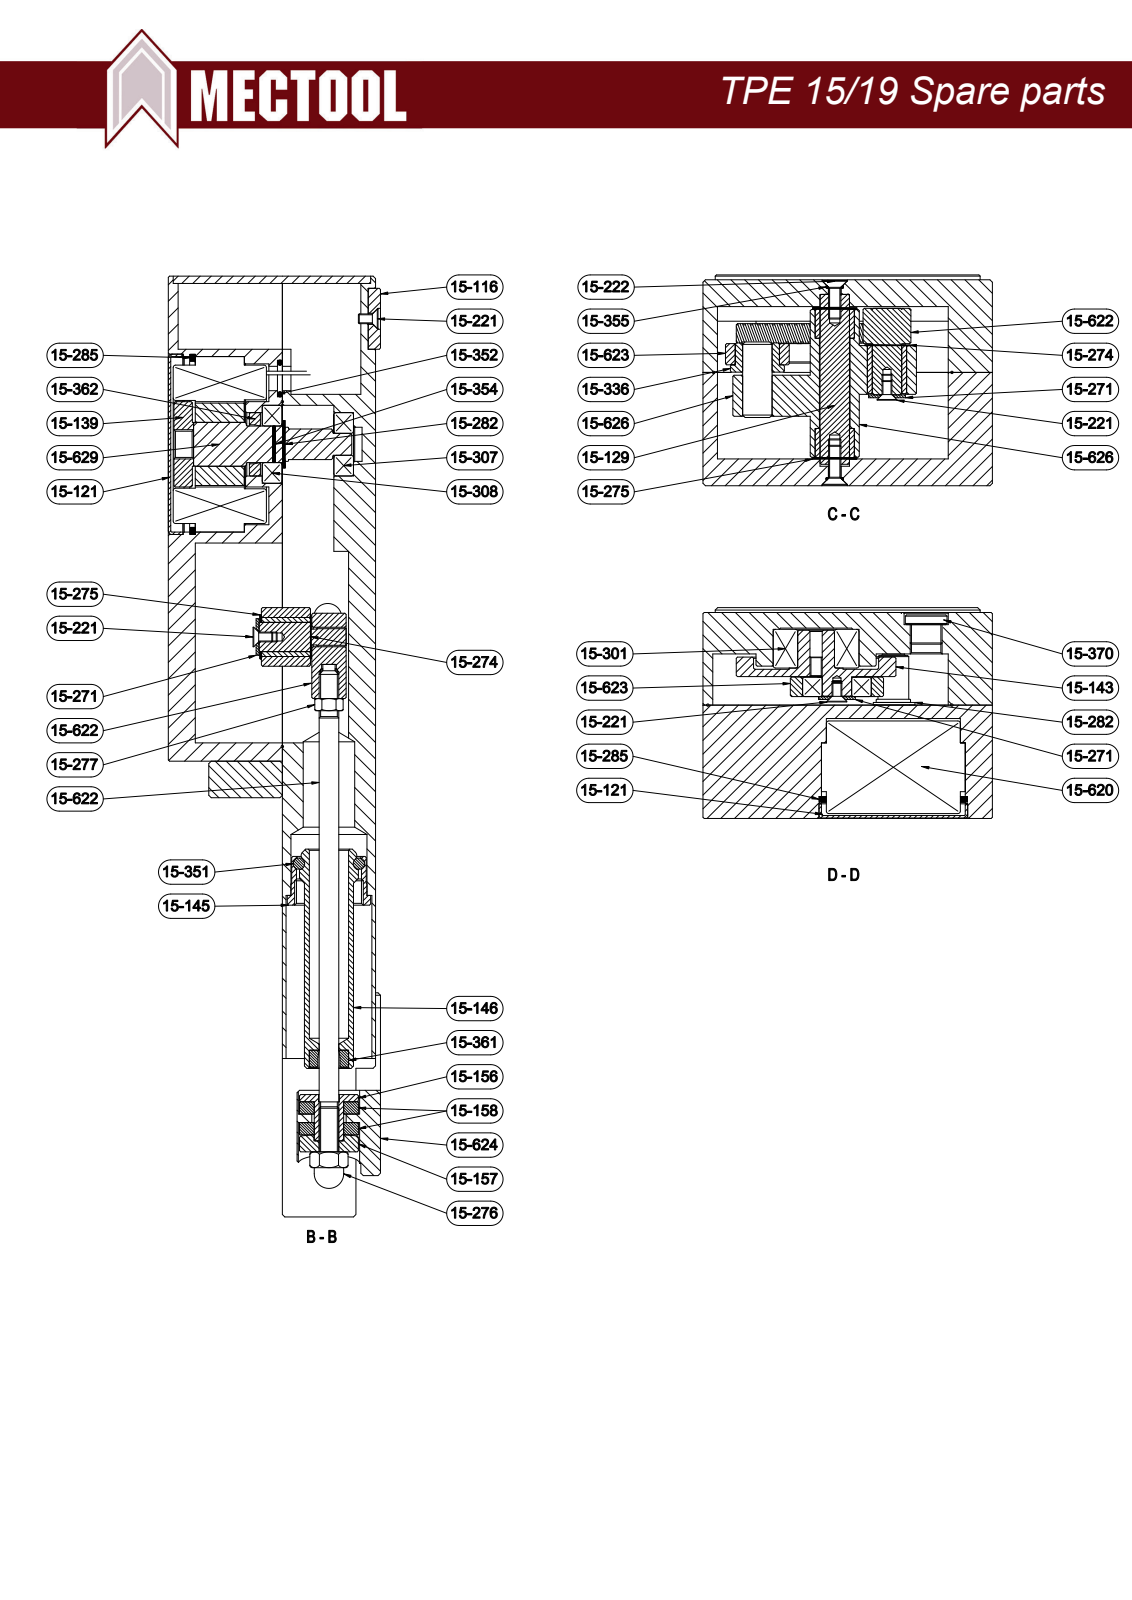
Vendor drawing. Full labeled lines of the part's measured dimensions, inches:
Part name (STEP PRODUCT): Nut : Dome - M8,0 x 162,052; Bolt : Hex - M4,0 x 12,0; Screw : Cheese - M6,0 x 10,0
STEP written by: Spatial InterOp 3D (automotive_design)
Units: inches
Bodies: 76 solids, 1832 faces (1675 planar, 128 cylindrical, 29 other)
Overall size (bounding box): 15.197 × 6.693 × 3.484
Volume: 162.7 in³ · Surface area: 545.2 in²
Round holes (diameter × count): ⌀0.354 ×10, ⌀0.197 ×9, ⌀0.165 ×6, ⌀0.315 ×6, ⌀0.394 ×5, ⌀0.295 ×4, ⌀0.421 ×4, ⌀0.591 ×4, ⌀0.346 ×3, ⌀0.15 ×2, ⌀0.236 ×2, ⌀0.512 ×2
Round bosses / shafts (diameter × count): ⌀0.347 ×11, ⌀0.236 ×4, ⌀0.315 ×2, ⌀0.984 ×1, ⌀0.787 ×1, ⌀0.578 ×1, ⌀0.394 ×1
Partial cylindrical surfaces — rounded edges, fillets, slot ends (radius × count): R0.276 ×6, R0.157 ×4, R0.236 ×2, R0.433 ×2, R0.787 ×1
Main face-to-face distances: 1.496, 4.646, 3.327, 1.831, 0.079, 0.394, 0.787, 7.402, 0.276, 0.118
Hole centre spacings: 3.858, 1.772, 4.246, 3.543, 4.036, 5.748, 13.15, 0.062
